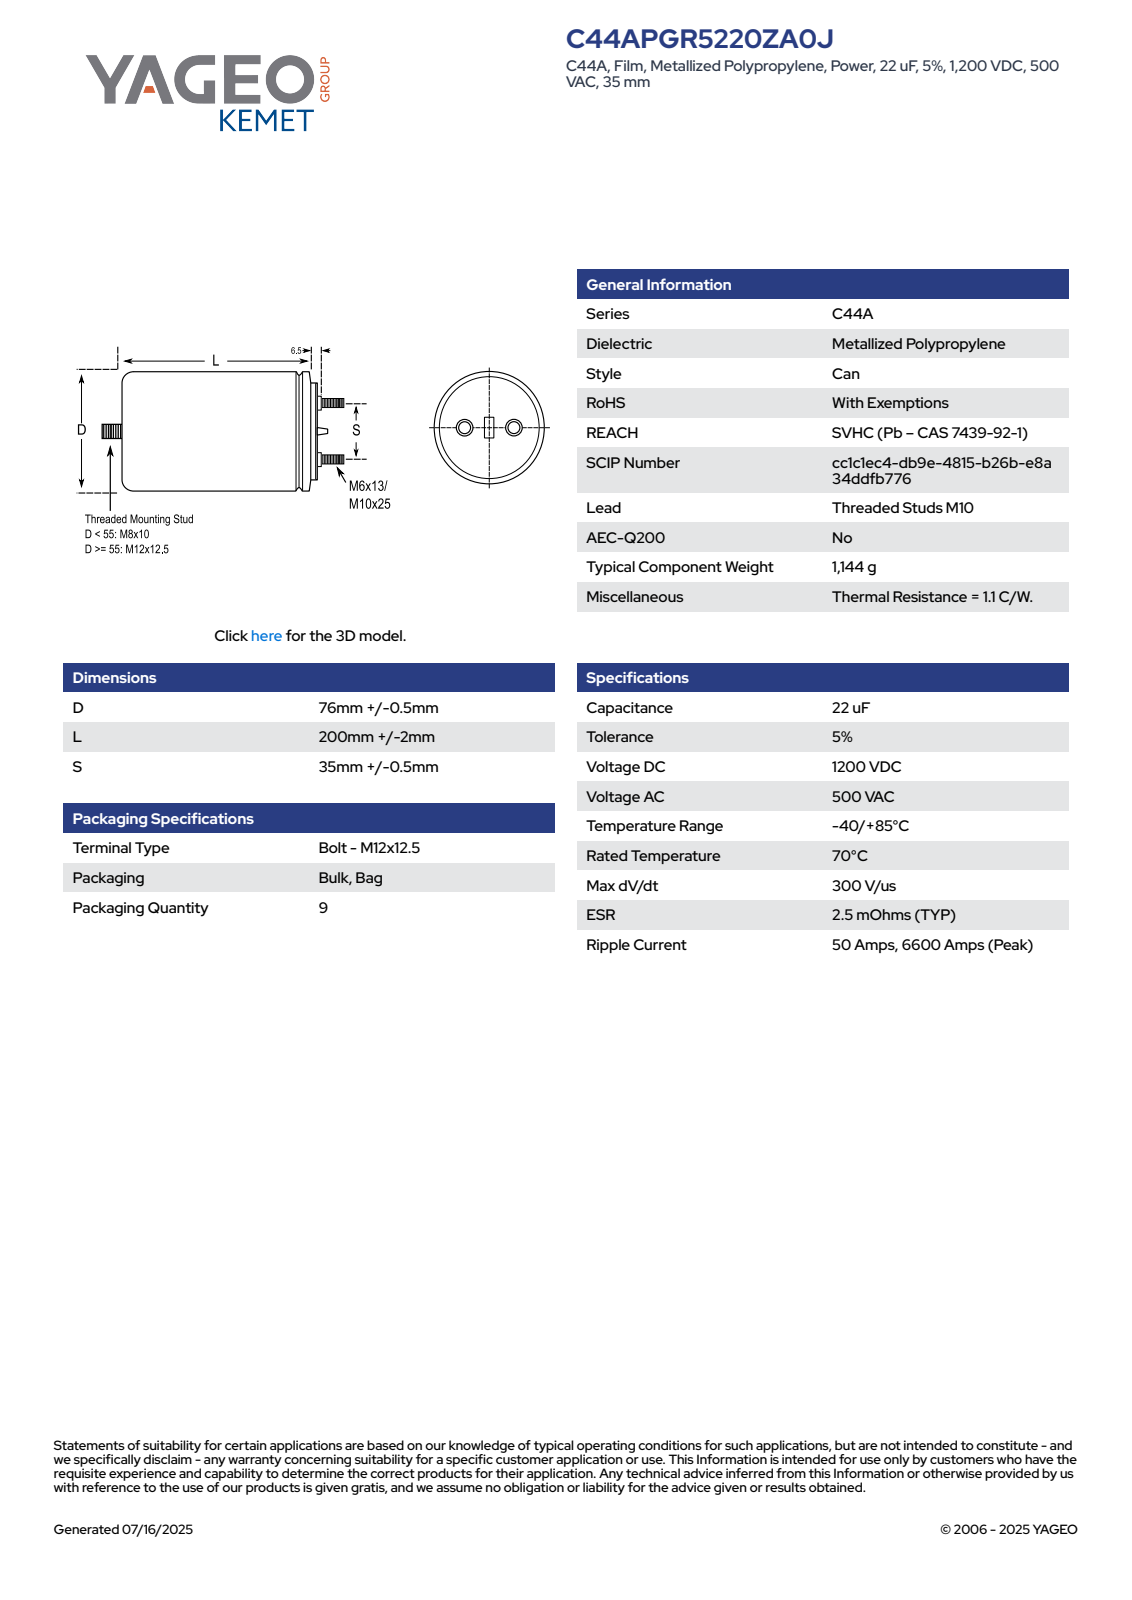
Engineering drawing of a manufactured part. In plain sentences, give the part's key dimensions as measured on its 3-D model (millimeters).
The part is named "CFP_C44A_76X200_D76.5L202S35". Its 3-D file was written by "SolidWorks 2014 (AUTOMOTIVE_DESIGN)". It is 1 solid with 102 faces: 29 planar, 34 cylindrical and 39 other. Overall it measures 234 by 76.5 by 76.5 millimeters. Its volume is 936 963 cubic millimeters and its surface area 58 855 square millimeters. Round bosses or shafts: 2 of diameter 9, 2 of diameter 6, 1 of diameter 76.5, 1 of diameter 60, 1 of diameter 12. Partial cylindrical surfaces (rounded edges, fillets, slot ends): 1 of radius 38.24. The main face-to-face distances are 207, 12.5, 219.5, 221, 208.5, 1.5, 234, 221.5, 14.5, 13.
